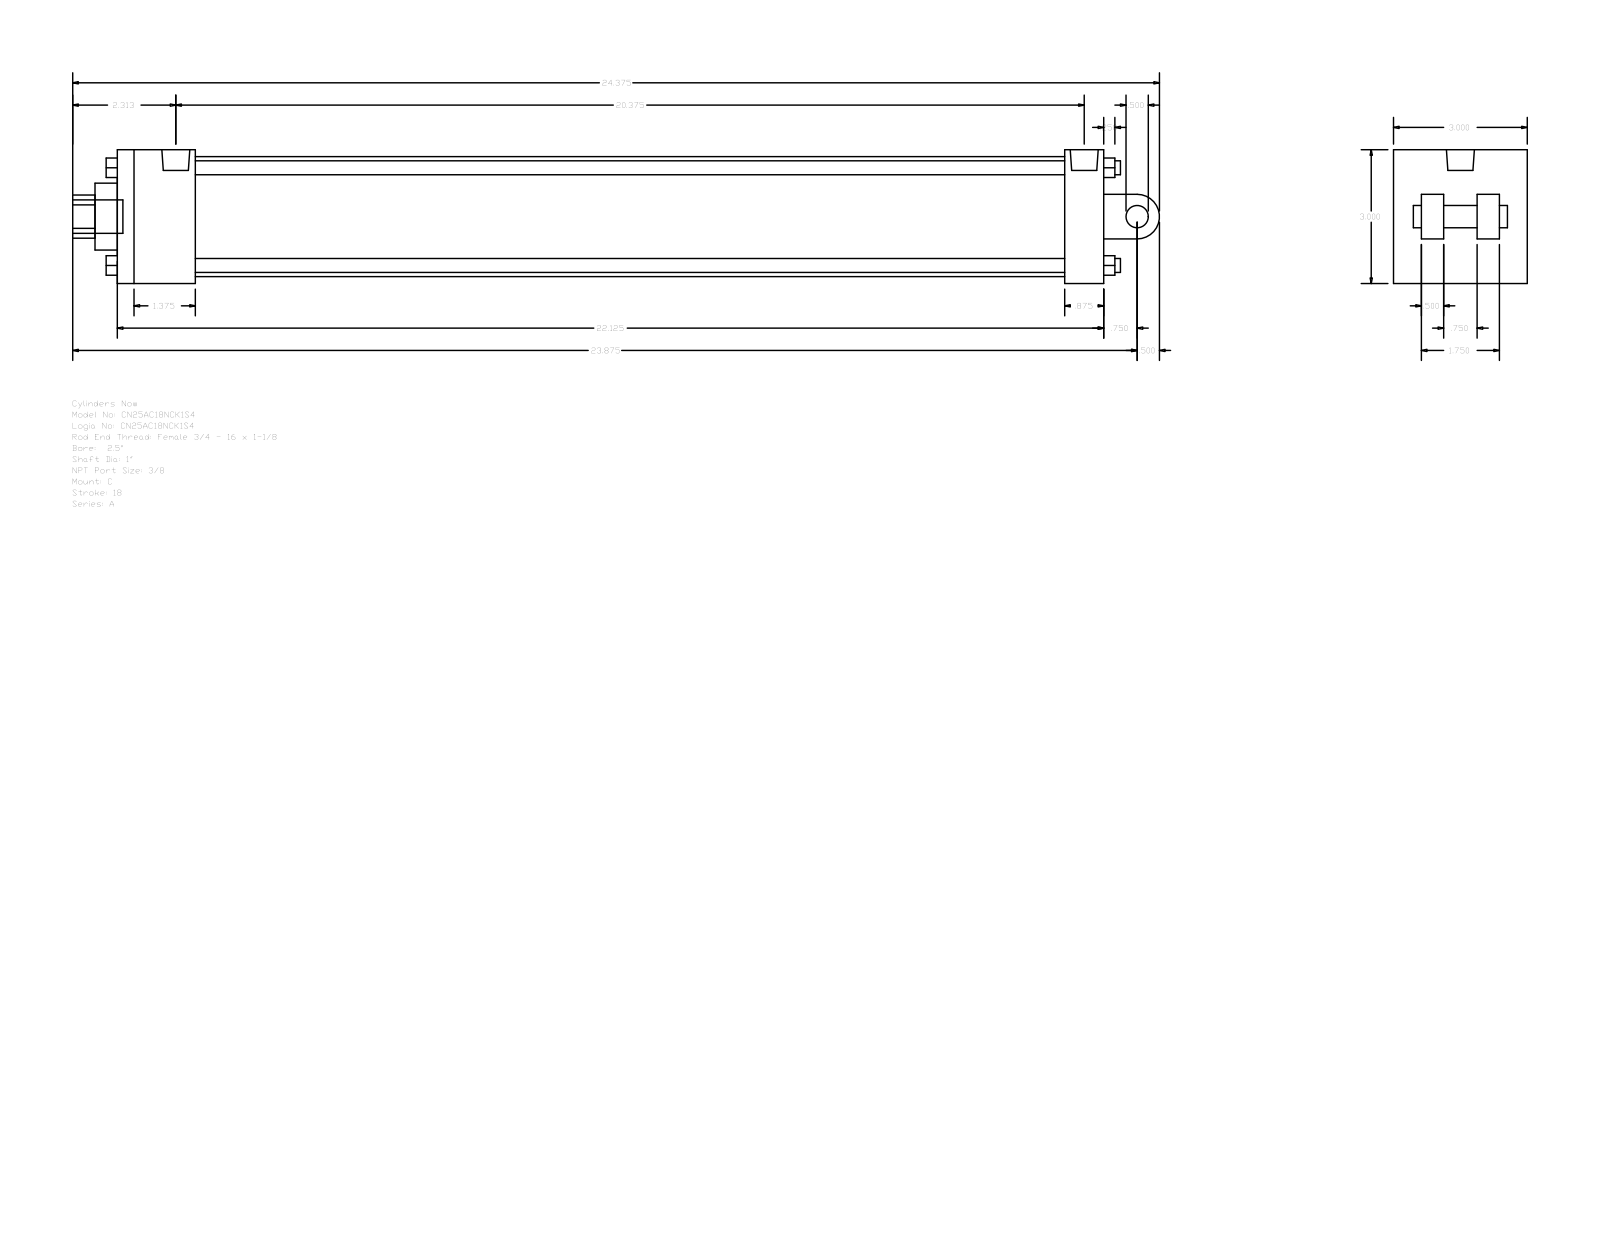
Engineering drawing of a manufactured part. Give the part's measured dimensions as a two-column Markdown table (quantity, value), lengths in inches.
| quantity | value |
| --- | --- |
| part name | A_C__0250_1 |
| STEP written by | GSSL Pune (CONFIG_CONTROL_DESIGN) |
| units | inches |
| bodies | 0 solids, 135 faces (102 planar, 33 cylindrical, 0 other) |
| overall size | 24.375 × 3 × 3 |
| round holes (diameter × count) | 0.219 × 2, 0.627 × 1, 1 × 1, 1.5 × 1, 2.69 × 1 |
| round bosses / shafts (diameter × count) | 0.313 × 4, 0.219 × 2, 0.75 × 1, 0.627 × 1, 0.5 × 1 |
| partial cylindrical surfaces (radius × count) | 0.484 × 1, 0.5 × 1 |
| main face-to-face distances | 3, 22.125, 0.5, 1.75, 21.25, 19.5, 20.375, 0.875, 0.625, 1 |
| hole center spacings | 0.094 |
